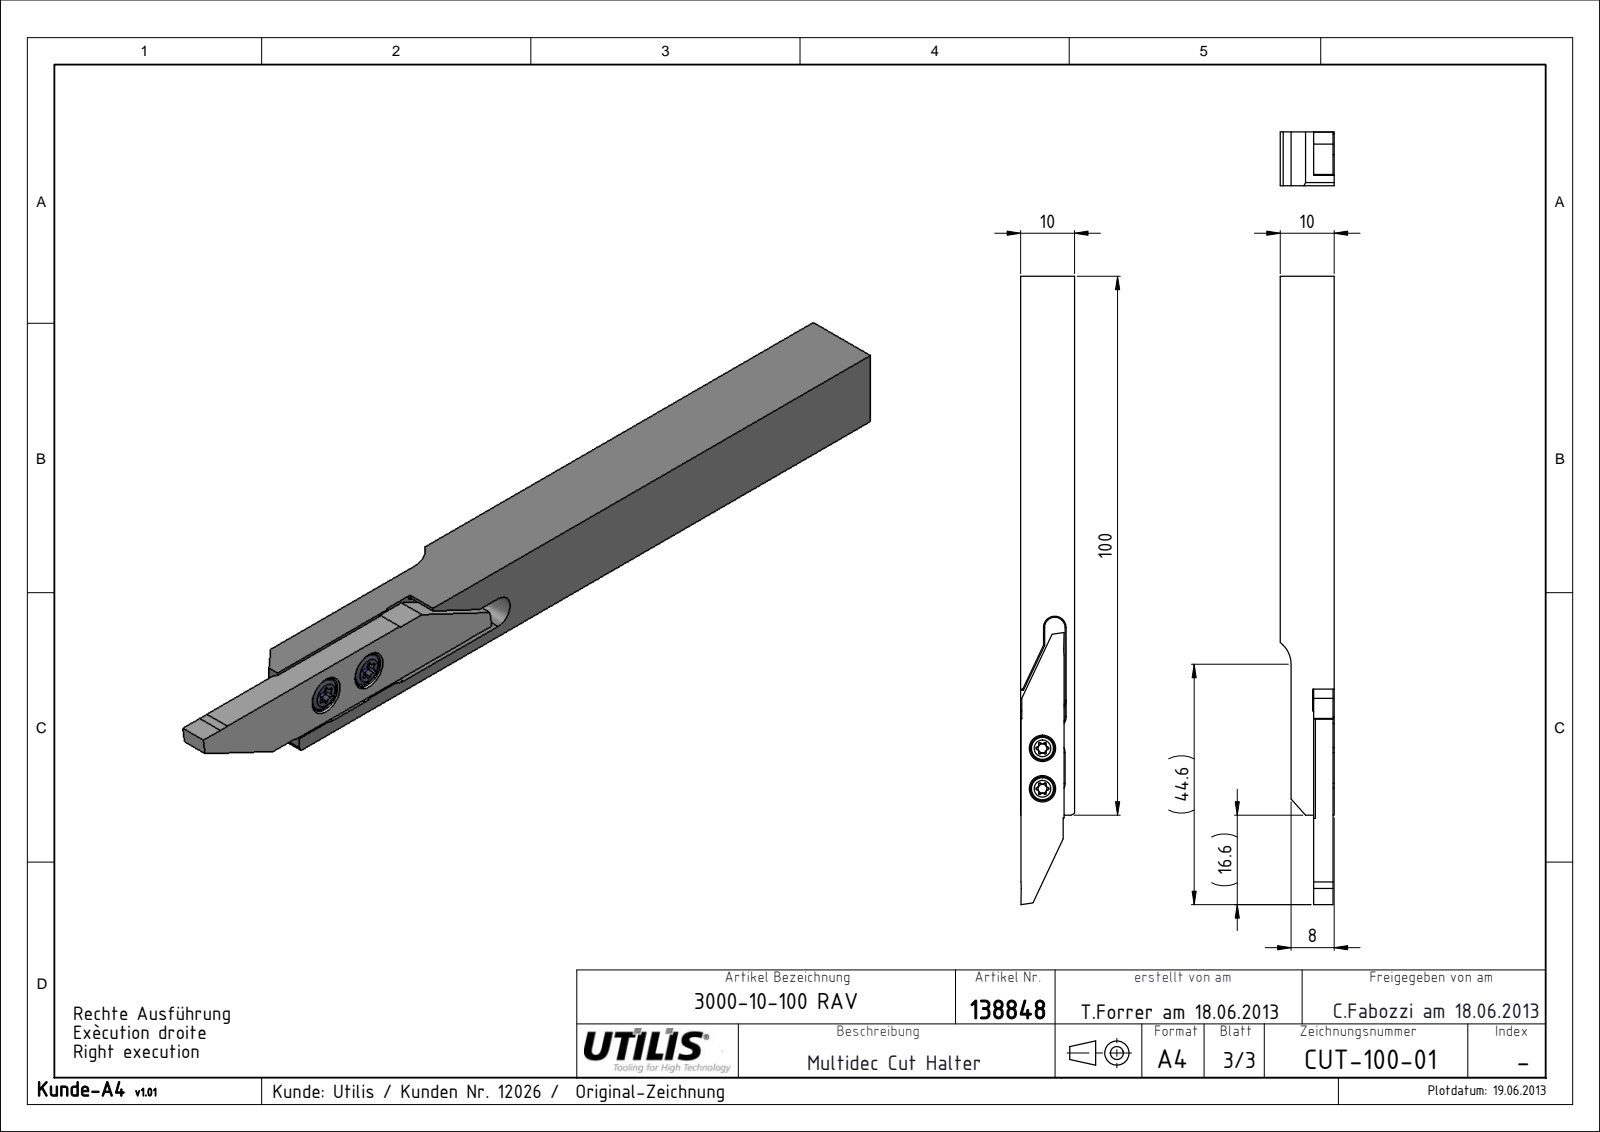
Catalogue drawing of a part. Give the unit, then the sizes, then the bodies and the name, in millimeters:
Units: millimetres
Overall size (bounding box): 116.6 × 10 × 10
Partial cylindrical surfaces — rounded edges, fillets, slot ends (radius × count): R0.2 ×12, R0.45 ×12, R2.1 ×4, R10 ×2, R5 ×1
Main face-to-face distances: 10, 8, 9.8, 2, 7.8, 4.2, 3.8, 6.2, 3.6, 9.95
Volume: 9 531 mm³ · Surface area: 4 636 mm²
Bodies: 1 solid, 77 faces (35 planar, 38 cylindrical, 4 other)
Part name (STEP PRODUCT): CUT-100-01
STEP written by: SolidWorks 2016 (AUTOMOTIVE_DESIGN)
